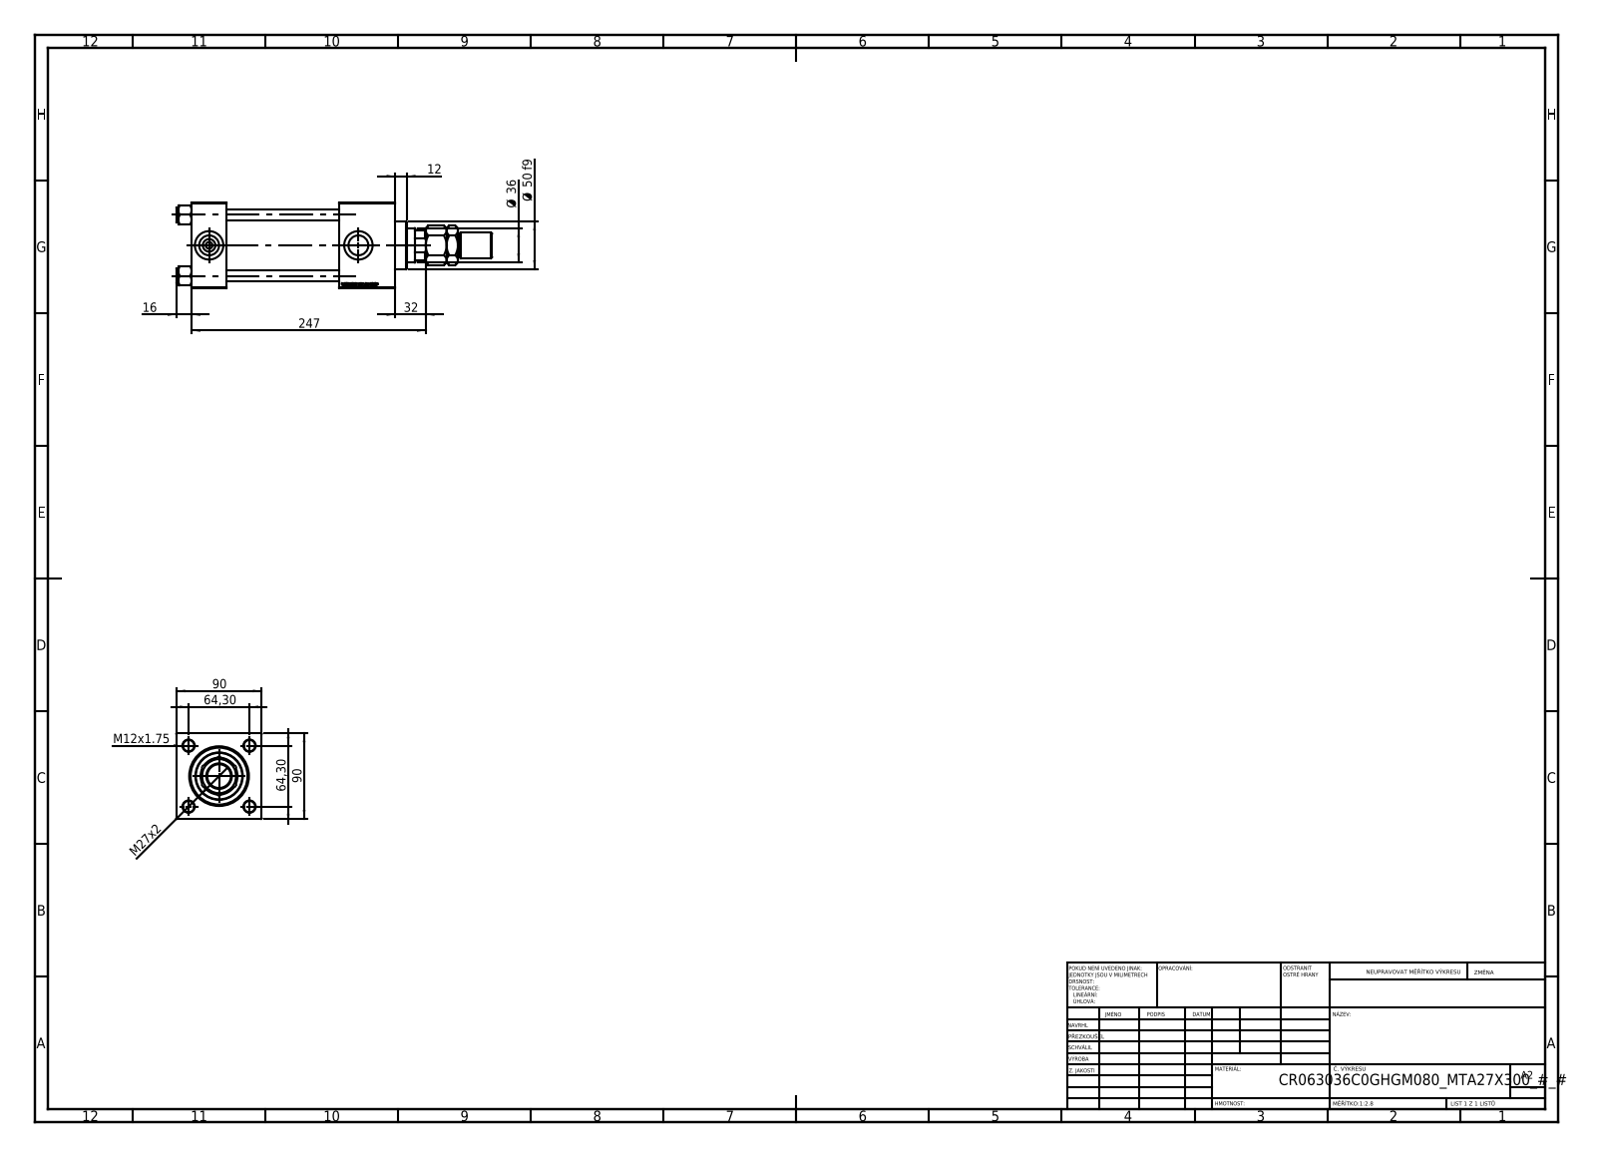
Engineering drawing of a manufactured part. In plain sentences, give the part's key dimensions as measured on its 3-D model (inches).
The part is named "V215CR_C_Body; V215CR_C_TYCINKA; MTA; V215CR_VCP_C (+2 more)". Its 3-D file was written by "SolidWorks 2019 (CONFIG_CONTROL_DESIGN)". It is 12 solids with 1197 faces: 541 planar, 90 cylindrical and 566 other. Overall it measures 13.11 by 3.543 by 3.543 inches. Its volume is 70.3 cubic inches and its surface area 363.3 square inches. Round holes: 4 of diameter 0.472, 2 of diameter 0.276, 2 of diameter 0.825, 2 of diameter 1.181, 1 of diameter 1.004, 1 of diameter 1.417, 1 of diameter 1.535, 1 of diameter 1.969, 1 of diameter 2.362, 1 of diameter 2.48. Round bosses or shafts: 4 of diameter 0.591, 1 of diameter 2.717, 1 of diameter 1.063, 1 of diameter 0.984. Partial cylindrical surfaces (rounded edges, fillets, slot ends): 1 of radius 0.689. The main face-to-face distances are 3.543, 1.457, 8.465, 7.008, 2.323, 6.142, 4.685, 7.335, 5.878, 1.193. The hole center spacings are 1.79, 2.531, 3.58, 6.201.
